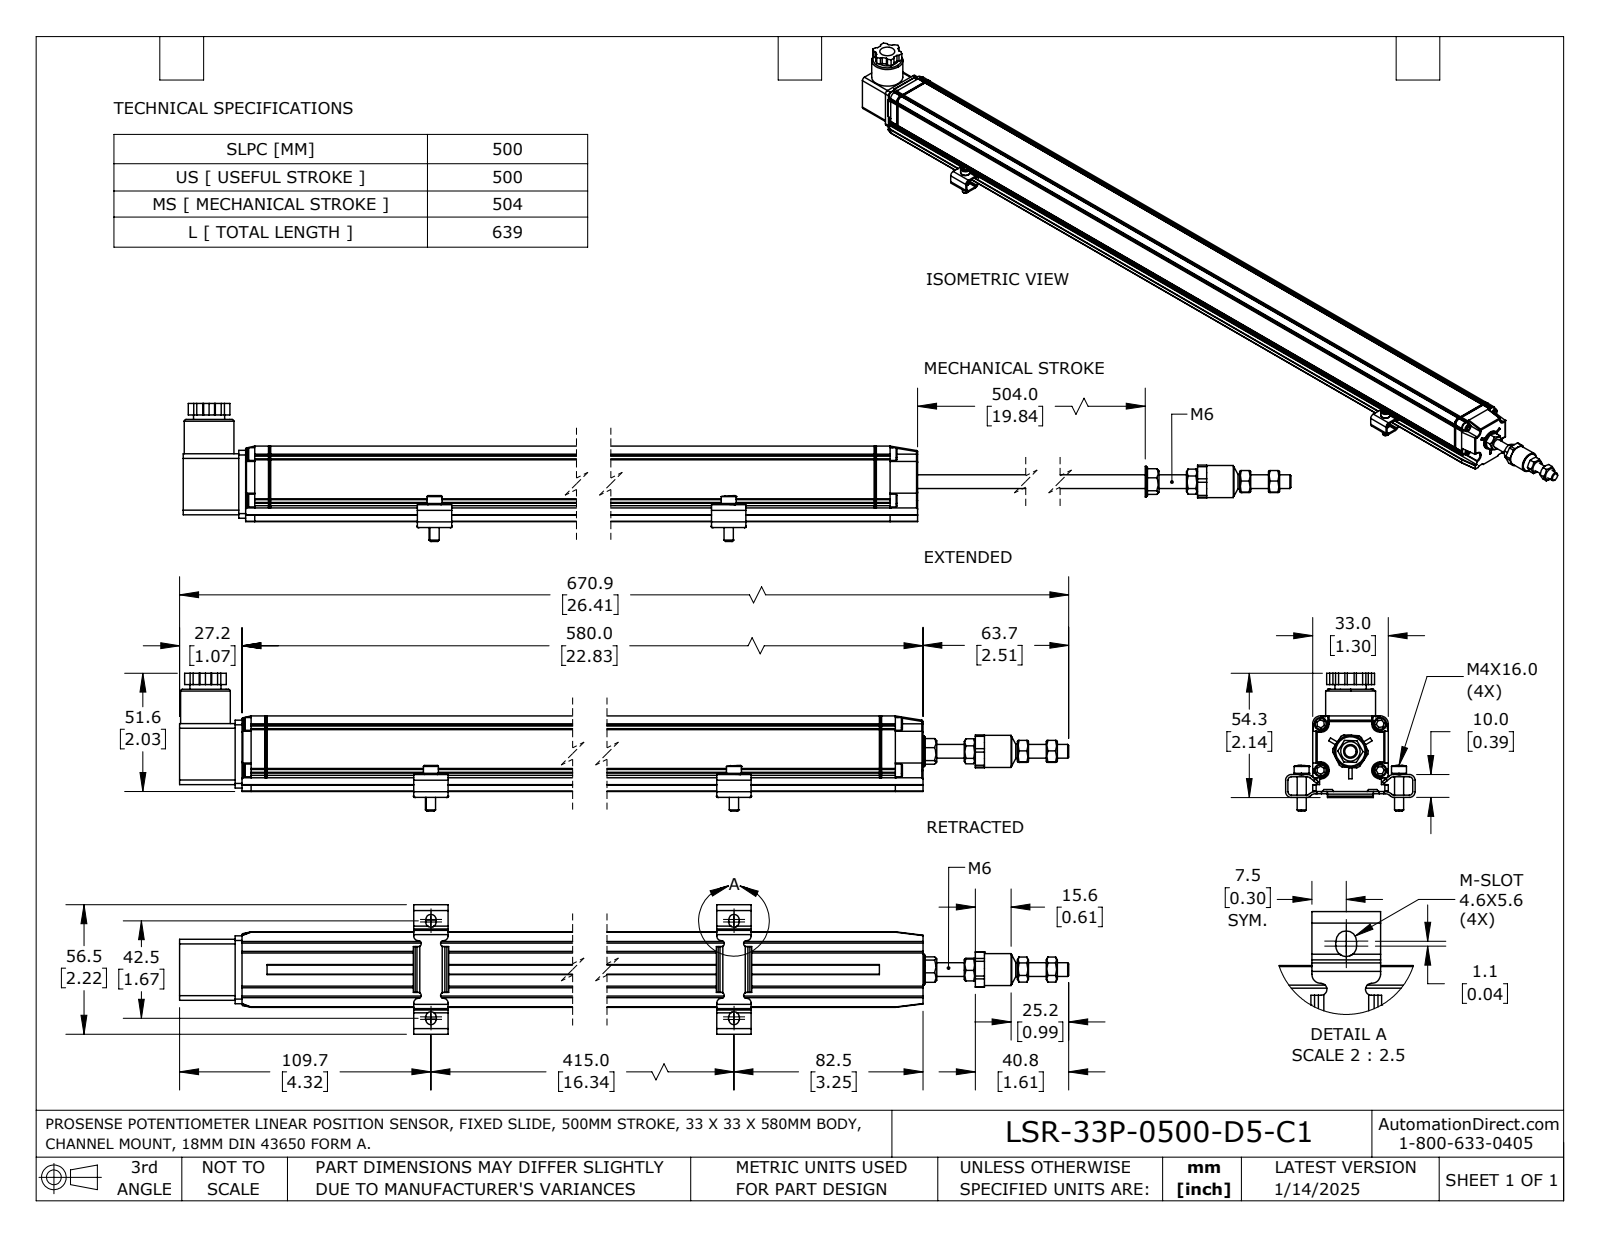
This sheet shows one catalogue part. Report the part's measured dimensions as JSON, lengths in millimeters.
{"part_name": "LSR-33P-0500-D5-C1", "step_written_by": "SolidWorks 2023 (AUTOMOTIVE_DESIGN)", "units": "millimeters", "bodies": {"solids": 14, "faces": 995, "planar": 641, "cylindrical": 269, "other": 85}, "overall_size": [670.8, 60.2, 56.5], "volume_mm3": 587600, "surface_area_mm2": 145400, "round_holes": [[2.7, 4], [3.3, 4], [4.3, 1], [5.2, 1], [5.3, 1], [5.9, 1], [7, 1], [7.2, 1], [10, 1], [10.5, 1], [14.6, 1], [15.3, 1]], "round_bosses_or_shafts": [[4, 5], [3, 5], [6.5, 4], [5.6, 4], [21.7, 1], [14, 1], [13.6, 1], [13.4, 1]], "partial_cylinders_radius": [[2, 28], [0.5, 23], [0.2, 16], [1.3, 8], [1.5, 8], [2.3, 8], [3, 8], [1, 4]], "face_to_face_distances": [33, 3, 5.6, 30, 27.4, 1, 2, 3.6, 31, 4.7], "hole_center_spacings": [1.2, 14.8, 15.4, 17.7, 18.5, 20.3, 26, 33]}
